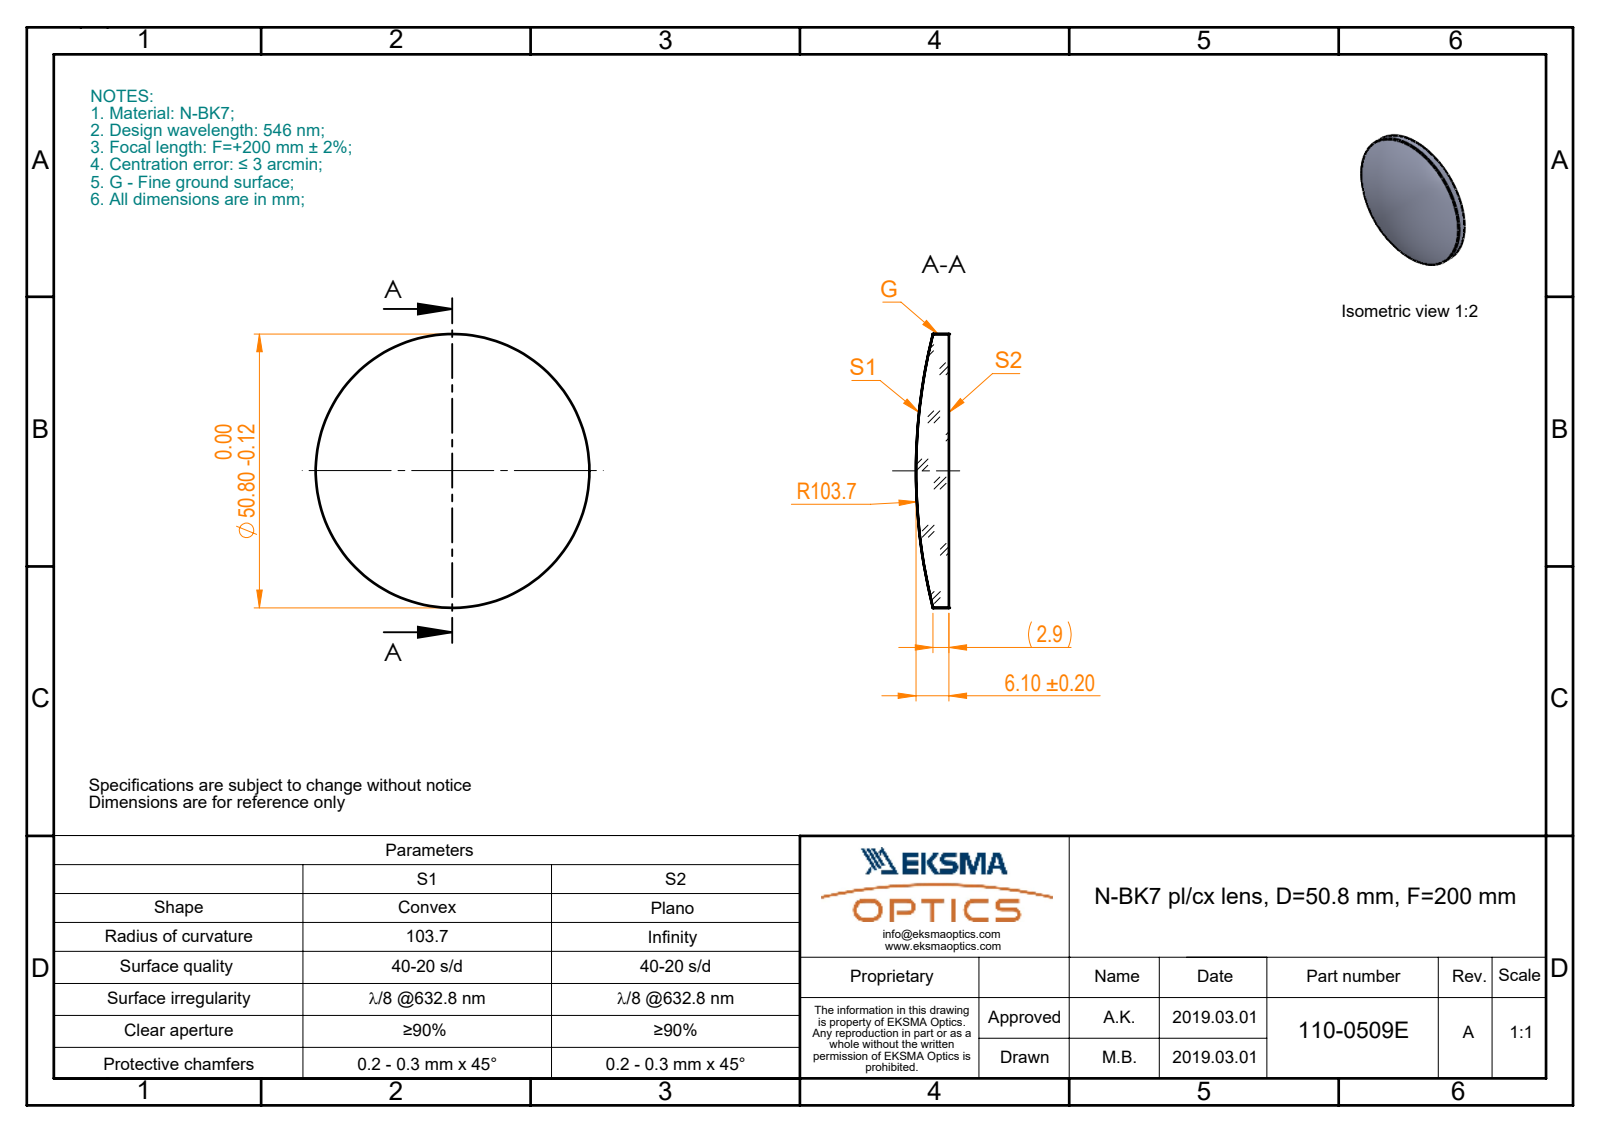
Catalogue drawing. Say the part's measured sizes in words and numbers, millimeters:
The part is named "110-0509E BK7 pl-cx 50.8 F200". Its 3-D file was written by "SolidWorks 2017 (CONFIG_CONTROL_DESIGN)". It is 1 solid with 5 faces: 1 planar, 2 cylindrical and 2 other. Overall it measures 50.8 by 50.8 by 6.1 millimeters. Its volume is 9 179 cubic millimeters and its surface area 4 554 square millimeters. Round bosses or shafts: 1 of diameter 50.8.
